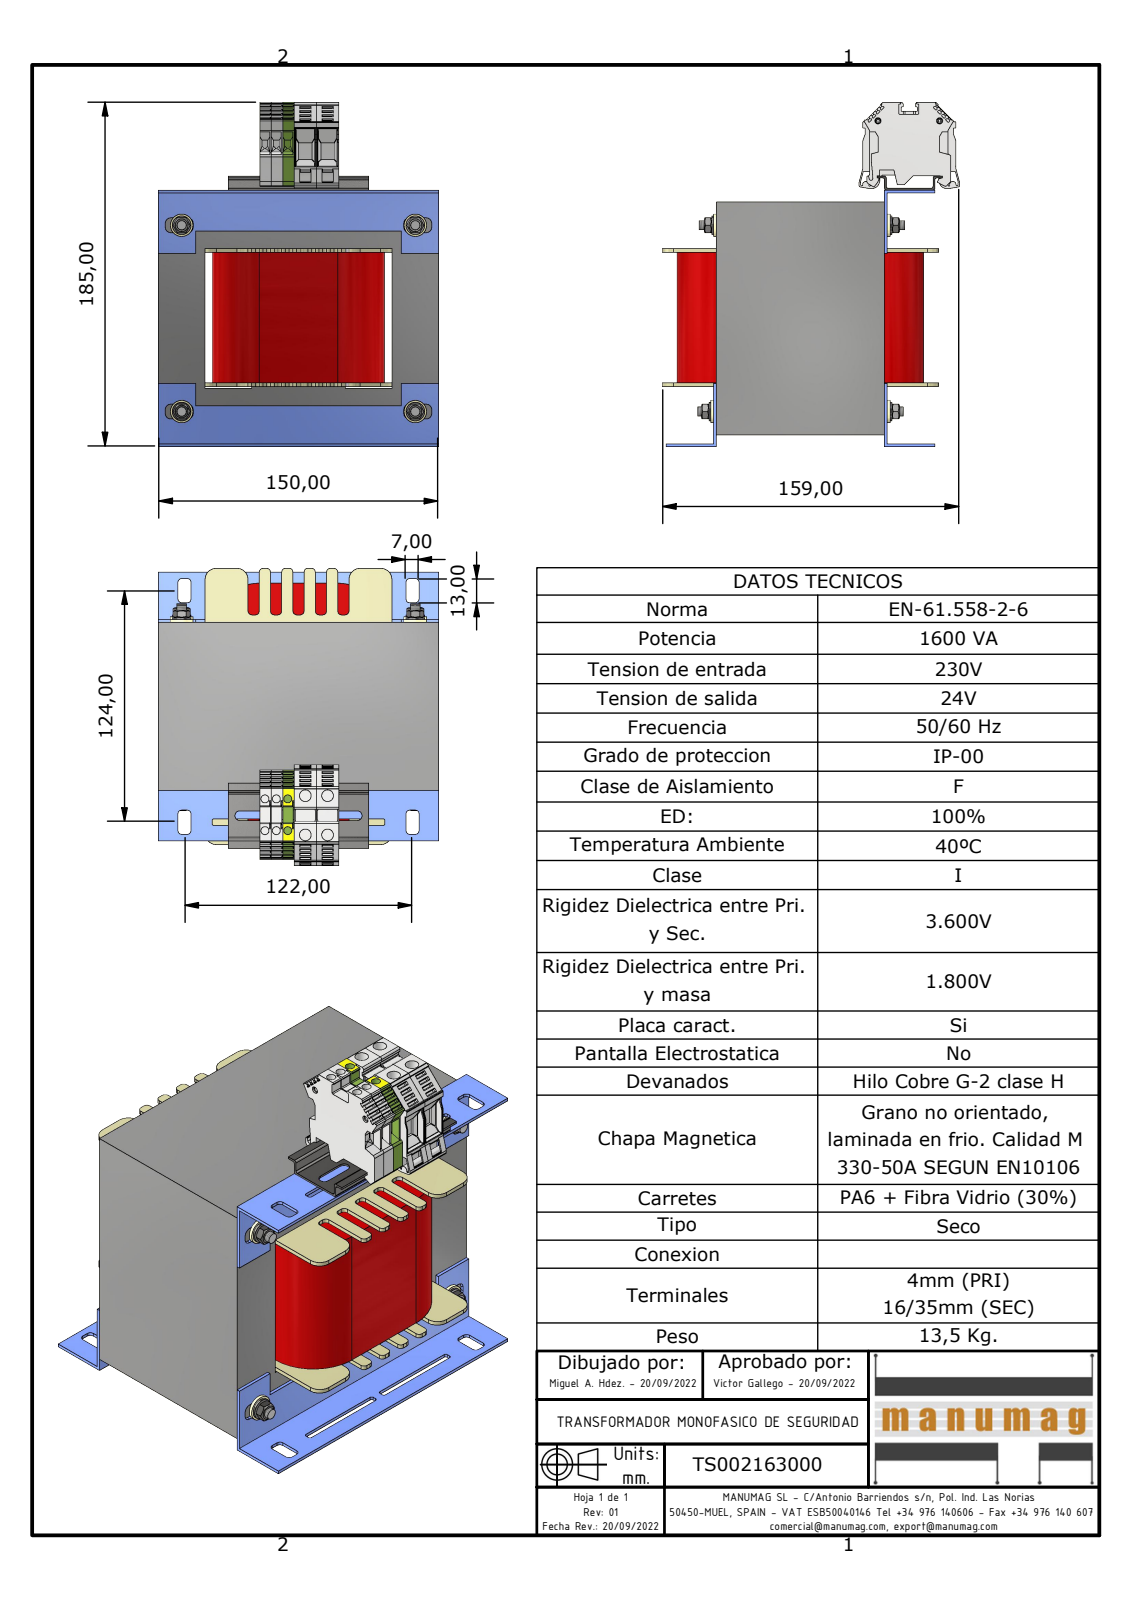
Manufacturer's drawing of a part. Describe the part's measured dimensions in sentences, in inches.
The part is named "TS002163000; EI150 x 125 - 90 (RC50); AF50DIN; centrador M5 (+8 more)". Its 3-D file was written by "Autodesk Inventor 2023 (AUTOMOTIVE_DESIGN)". It is 39 solids with 2333 faces: 1481 planar, 694 cylindrical and 158 other. Overall it measures 7.281 by 6.272 by 5.906 inches. Its volume is 120.5 cubic inches and its surface area 464.1 square inches. Round holes: 6 of diameter 0.169, 4 of diameter 0.163, 4 of diameter 0.197, 4 of diameter 0.209, 4 of diameter 0.248, 4 of diameter 0.315, 2 of diameter 0.094, 2 of diameter 0.098, 2 of diameter 0.108, 2 of diameter 0.116. Round bosses or shafts: 4 of diameter 0.472, 4 of diameter 0.394, 4 of diameter 0.232. Partial cylindrical surfaces (rounded edges, fillets, slot ends): 143 of radius 0.012, 55 of radius 0.079, 34 of radius 0.039, 32 of radius 0.01, 16 of radius 0.118, 9 of radius 0.02, 8 of radius 0.236, 6 of radius 0.102. The main face-to-face distances are 3.937, 0.984, 1.969, 4.921, 3.543, 0.059, 2.953, 0.827, 4.189, 0.252. The hole center spacings are 0.24, 0.711, 0.669, 0.469, 0.48, 0.824, 0.827, 0.95.
